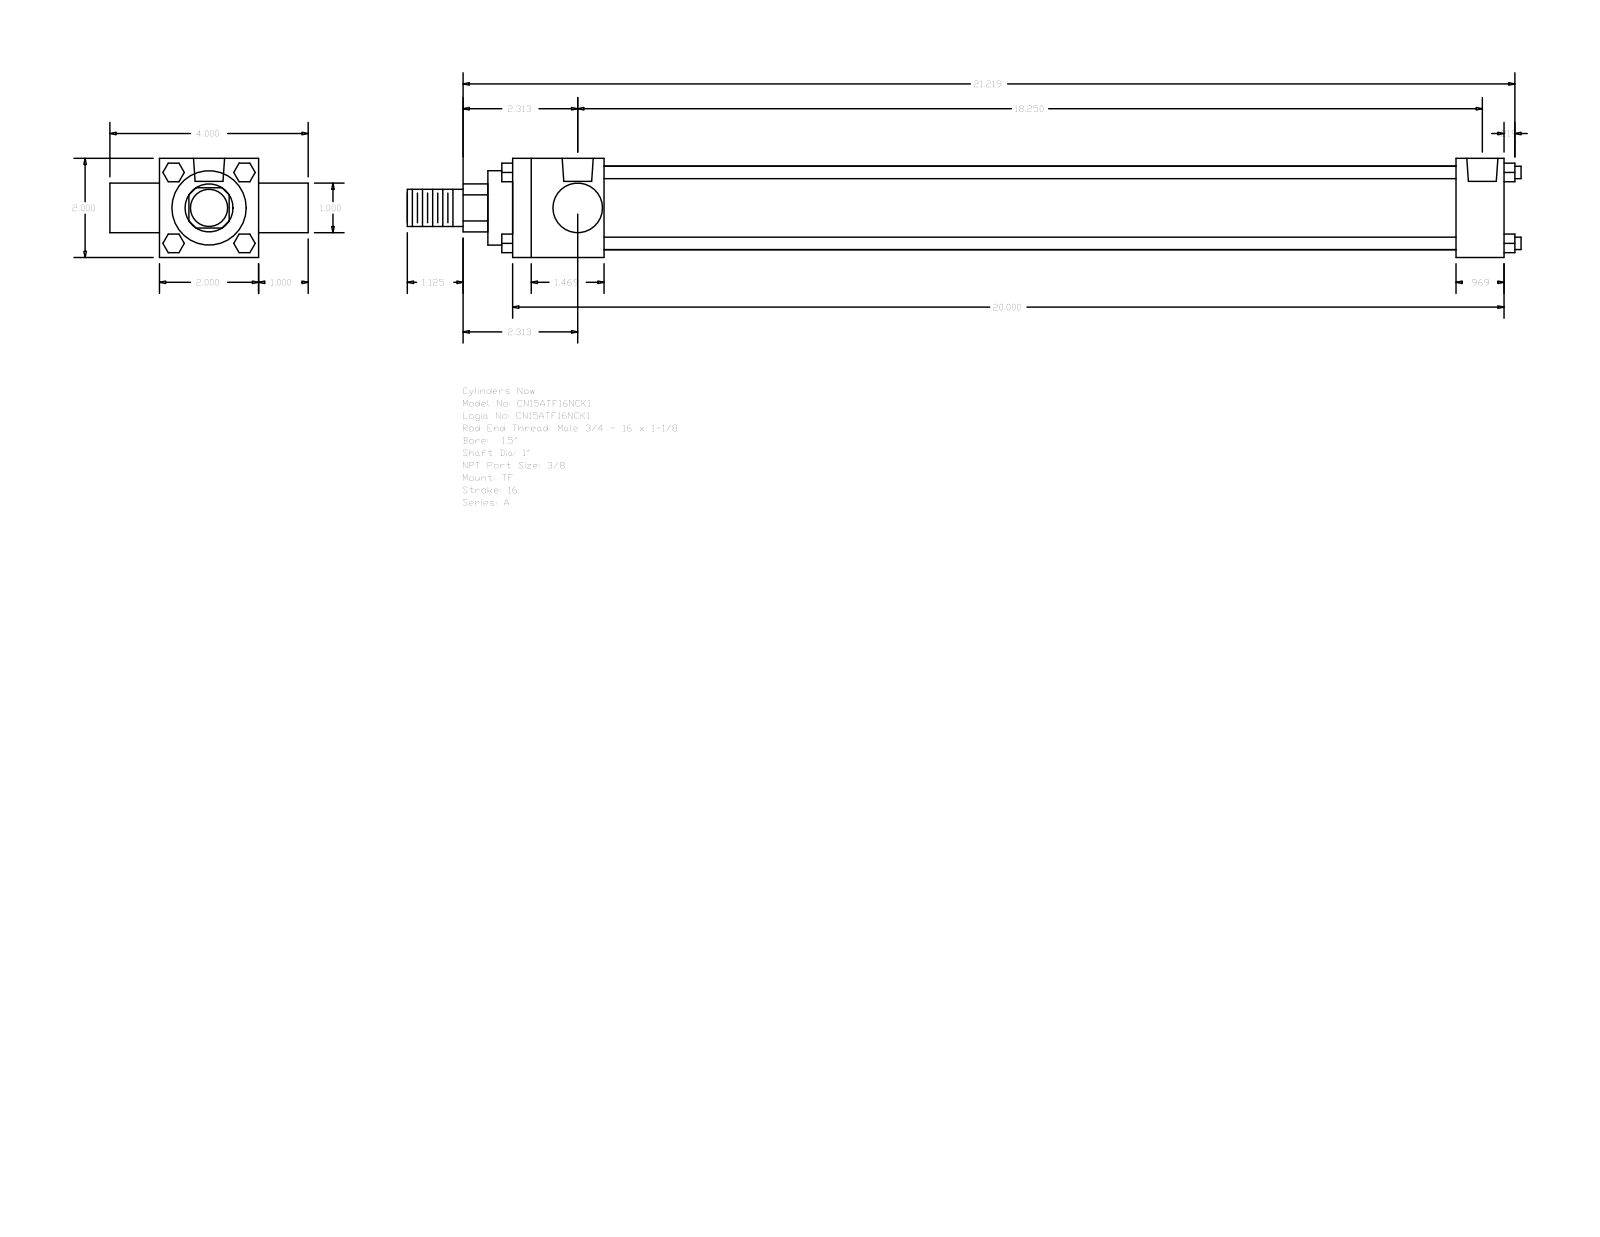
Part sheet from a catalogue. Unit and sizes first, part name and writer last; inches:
Units: inches
Overall size (bounding box): 22.469 × 4 × 2
Round holes (diameter × count): ⌀0.219 ×3, ⌀0.627 ×2
Round bosses / shafts (diameter × count): ⌀0.25 ×4, ⌀1 ×2, ⌀1.69 ×1, ⌀1.5 ×1, ⌀0.75 ×1
Partial cylindrical surfaces — rounded edges, fillets, slot ends (radius × count): R0.484 ×1
Main face-to-face distances: 2, 1, 20, 3, 1.844, 19.031, 17.187, 18.156, 0.969, 0.5
Hole centre spacings: 0.156, 18.094, 17.937, 18.25
Bodies: 0 solids, 120 faces (92 planar, 28 cylindrical, 0 other)
Part name (STEP PRODUCT): A_TF__0150_1
STEP written by: GSSL Pune (CONFIG_CONTROL_DESIGN)
